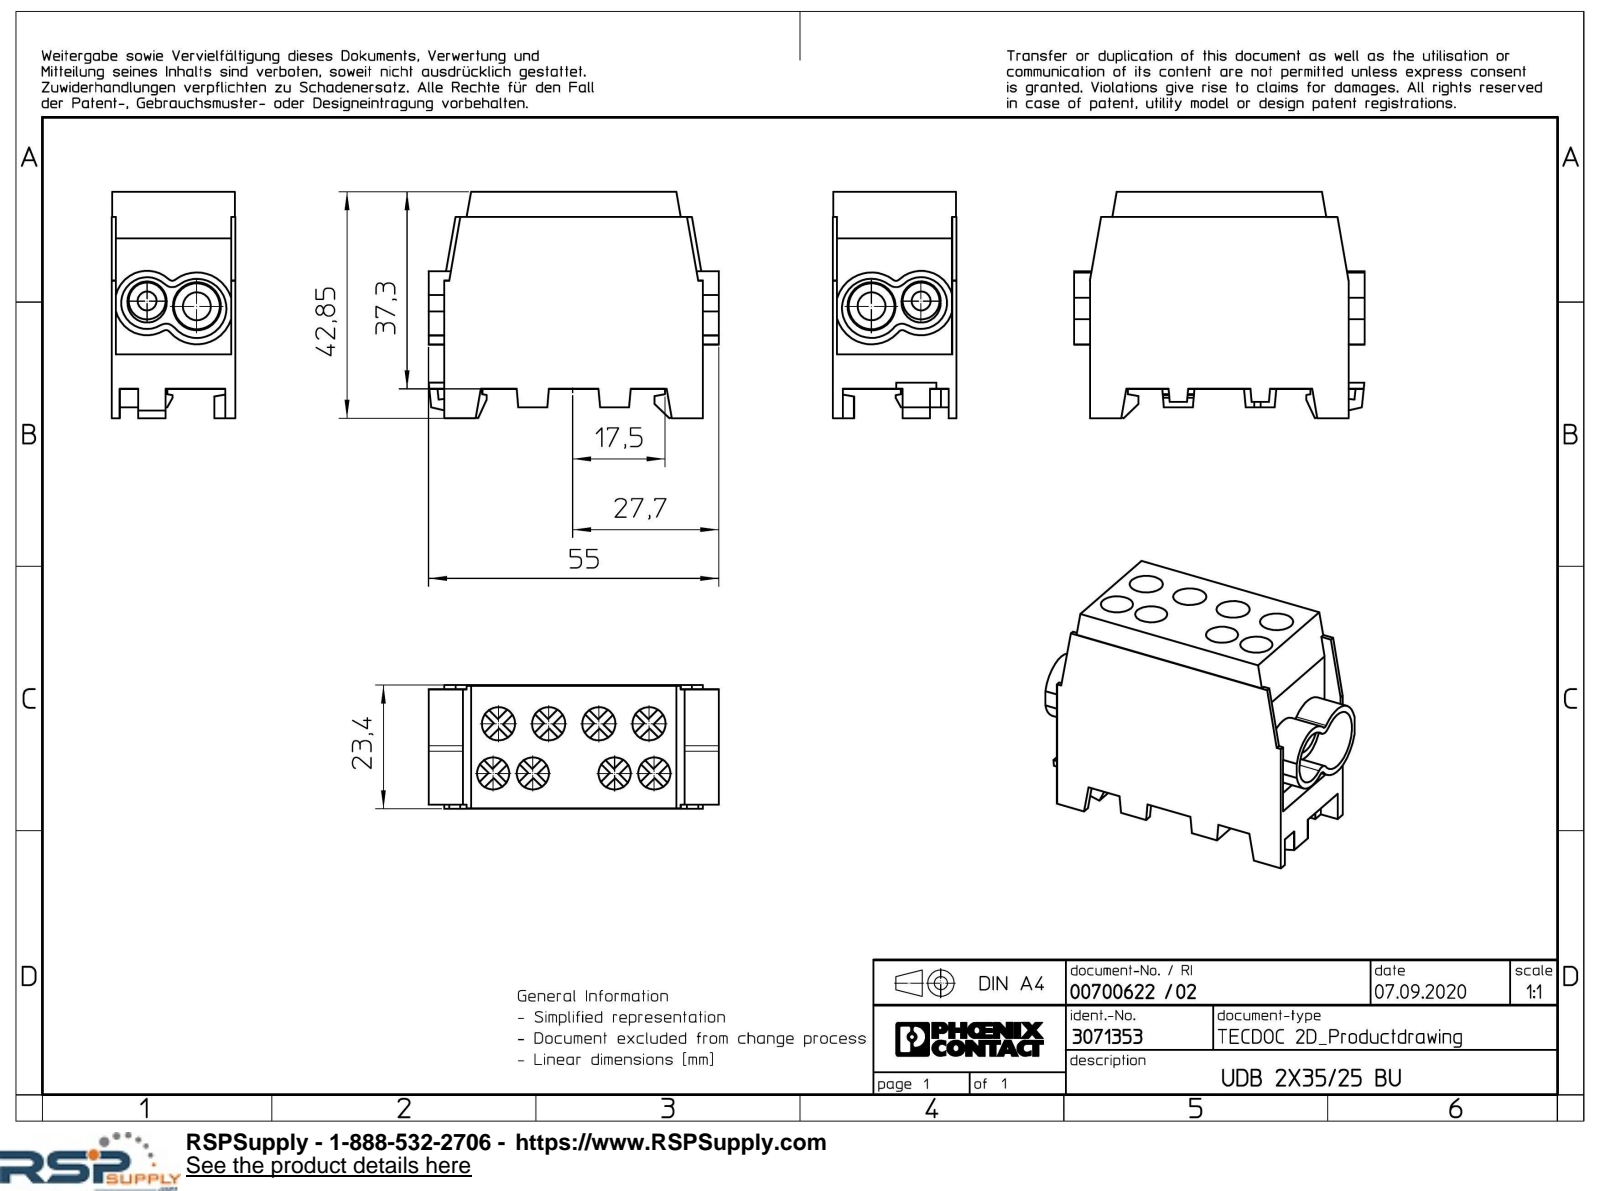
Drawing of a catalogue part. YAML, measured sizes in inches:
part_name: "UDB_2x35_25_BU-select"
step_written_by: "Creo Elements/Direct Modeling 20.1A 29-Sep-2018 (C) Parametric Technology GmbH (AUTOMOTIVE_DESIGN)"
units: inches
bodies: {solids: 1, faces: 275, planar: 209, cylindrical: 52, other: 14}
overall_size: [2.165, 1.687, 0.921]
volume: 2.073
surface_area: 20.46
round_holes:
  - {diameter: 0.24, count: 4}
  - {diameter: 0.248, count: 4}
  - {diameter: 0.276, count: 1}
  - {diameter: 0.343, count: 1}
  - {diameter: 0.358, count: 1}
partial_cylinders:
  - {radius: 0.031, count: 2}
  - {radius: 0.079, count: 2}
  - {radius: 0.146, count: 2}
  - {radius: 0.193, count: 1}
  - {radius: 0.22, count: 1}
  - {radius: 0.24, count: 1}
  - {radius: 0.268, count: 1}
face_to_face_distances: [0.921, 1.469, 0.138, 1.791, 0.917, 0.028, 0.031, 0.256, 0.89, 0.886]
hole_center_spacings: [0.372, 0.295, 0.45, 0.616, 0.87, 0.906, 0.942, 1.219]
